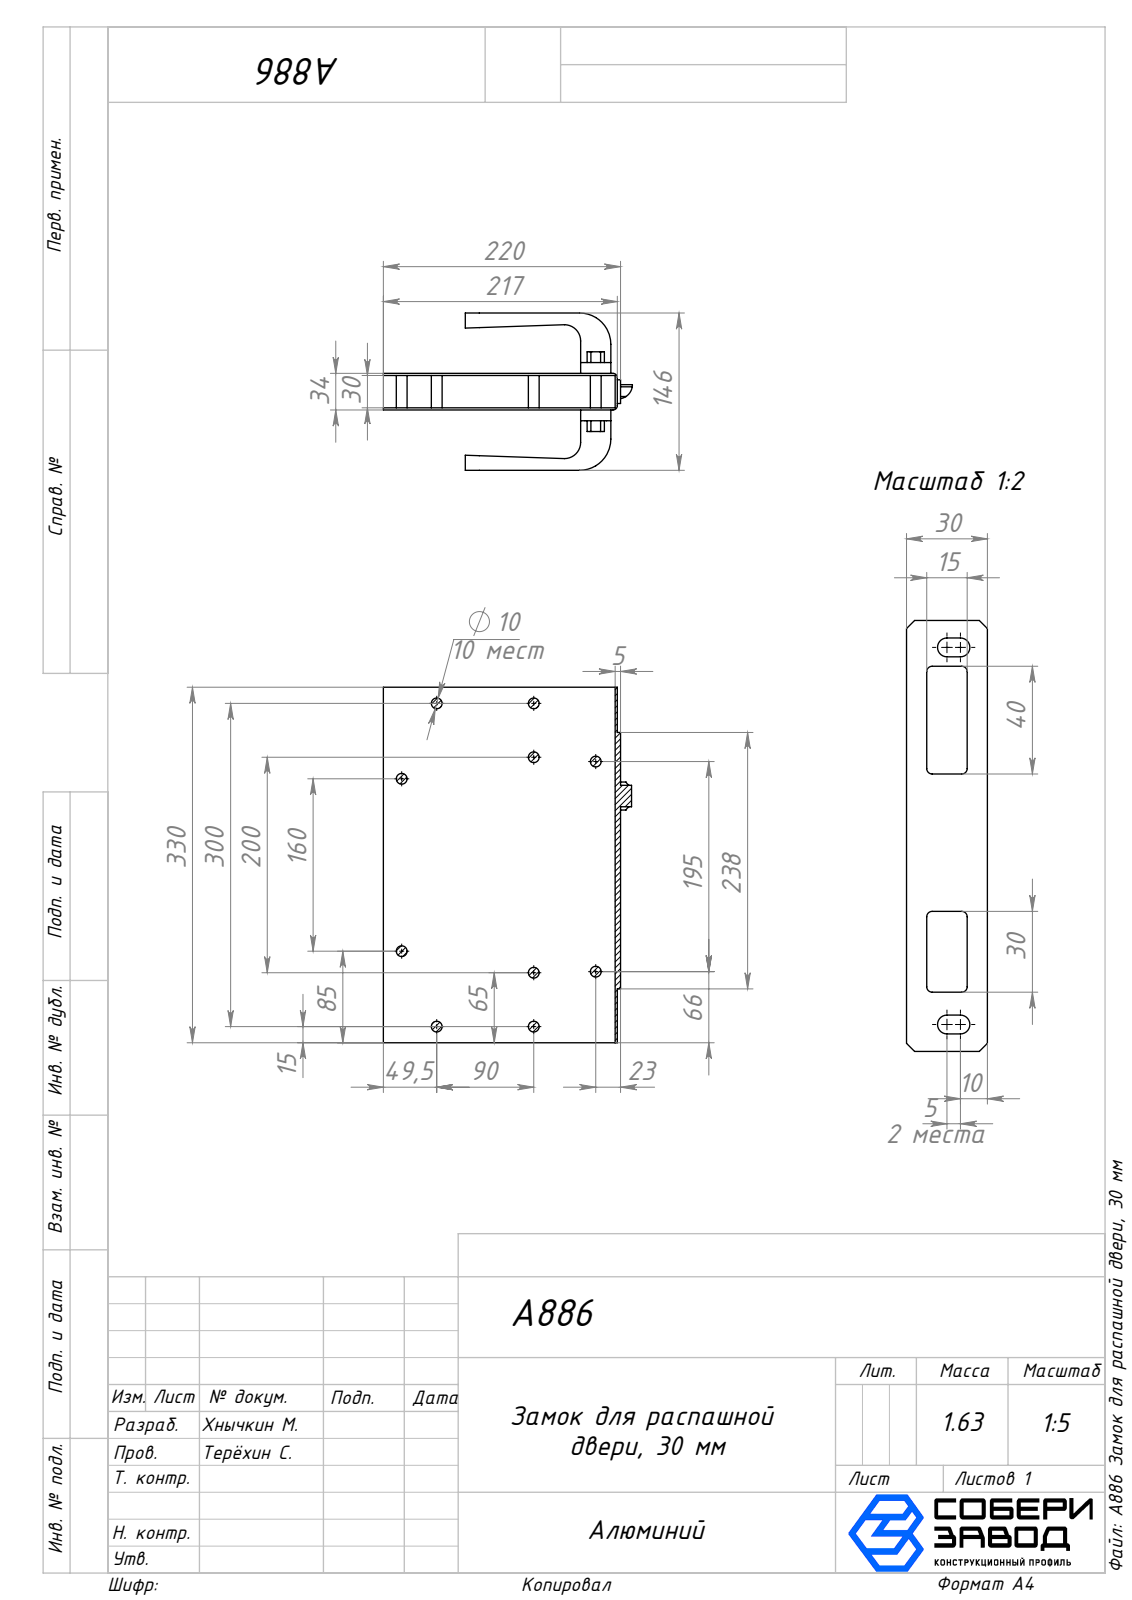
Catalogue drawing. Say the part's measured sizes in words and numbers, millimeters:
The part is named "A886 Замок для распашной двери, 30 мм". Its 3-D file was written by "SolidWorks 2025 (AUTOMOTIVE_DESIGN)". It is 1 solid with 101 faces: 48 planar, 53 cylindrical and 0 other. Overall it measures 330 by 231 by 146 millimeters. Its volume is 604 361 cubic millimeters and its surface area 354 247 square millimeters. Round bosses or shafts: 10 of diameter 10. Partial cylindrical surfaces (rounded edges, fillets, slot ends): 6 of radius 4, 2 of radius 1, 2 of radius 4.64, 2 of radius 5.49, 2 of radius 15.07, 2 of radius 29, 1 of radius 8, 1 of radius 13. The main face-to-face distances are 32, 2, 30, 34, 10, 42, 12, 44, 54, 28.
